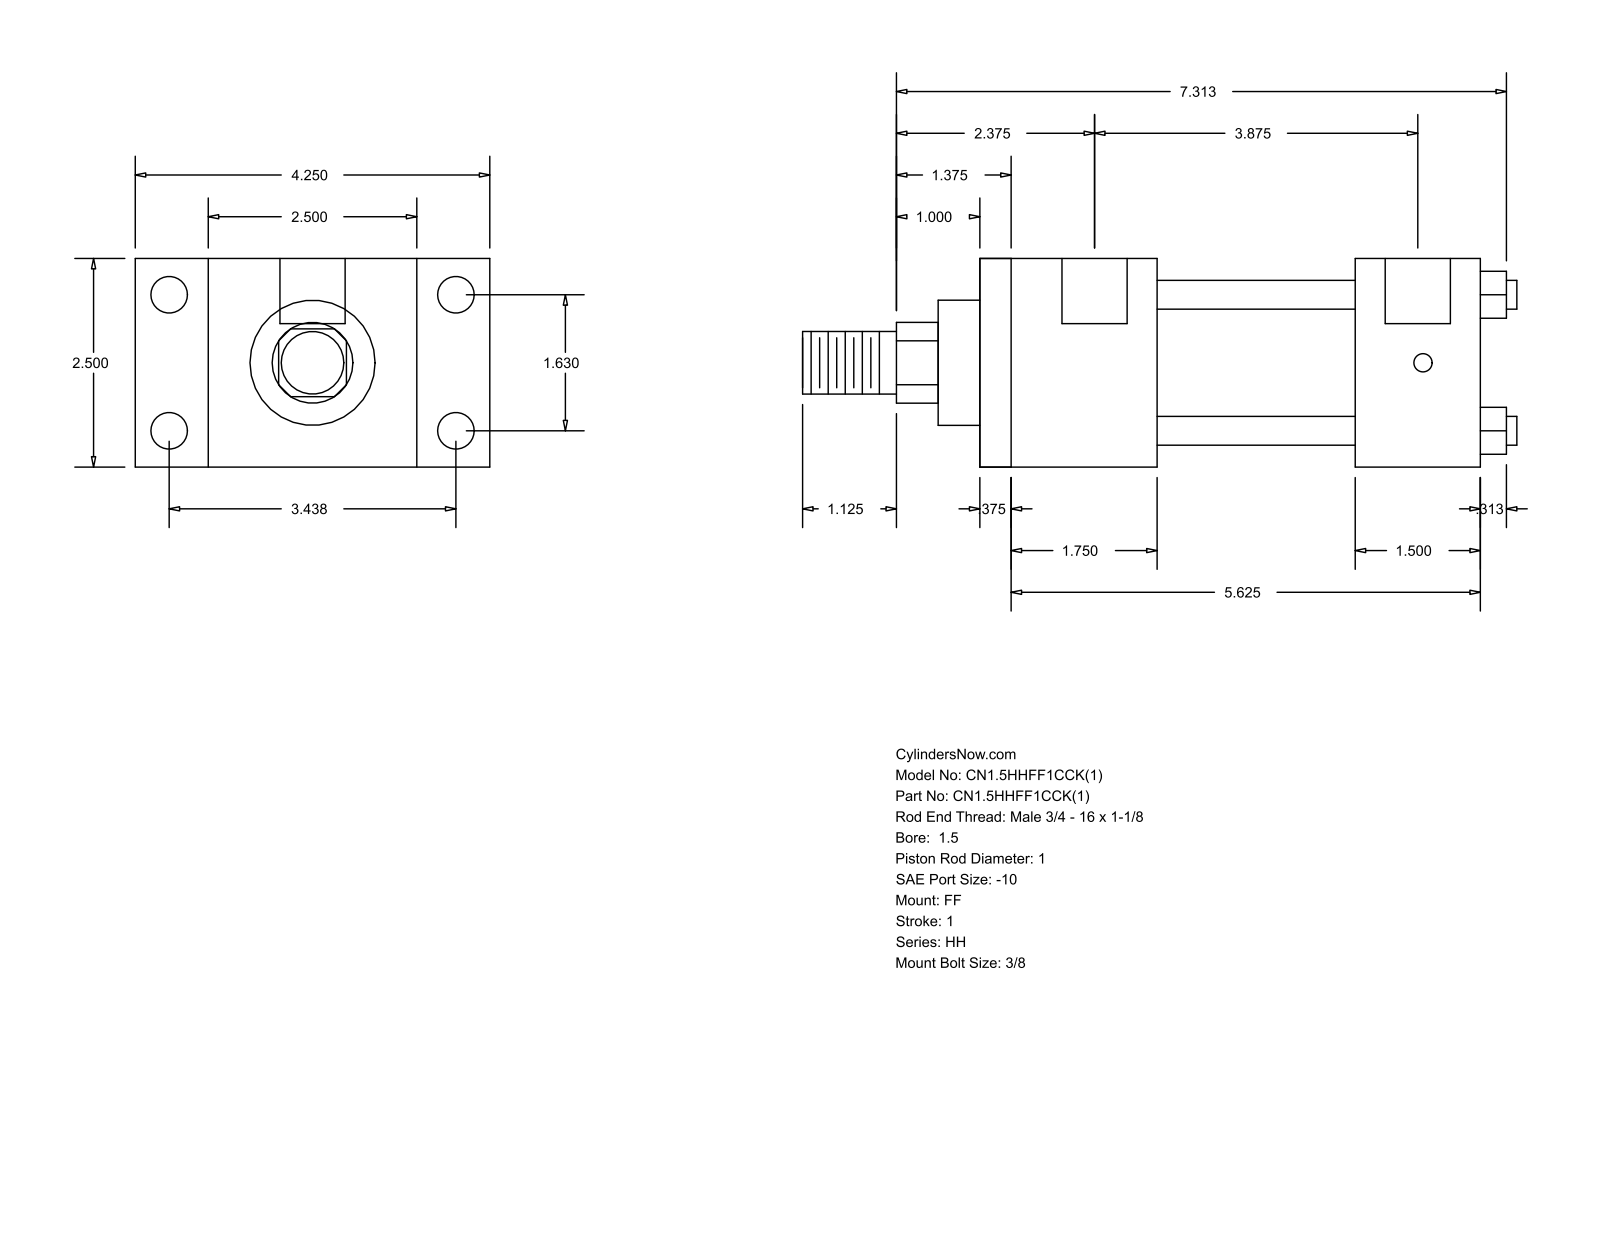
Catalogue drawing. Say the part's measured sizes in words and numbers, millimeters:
The part is named "HH_FF__0150_1". Its 3-D file was written by "GSSL Pune (CONFIG_CONTROL_DESIGN)". It is 0 solids with 92 faces: 64 planar, 28 cylindrical and 0 other. Overall it measures 217.49 by 107.95 by 63.5 millimeters. Round holes: 4 of diameter 5.56, 4 of diameter 11.13, 2 of diameter 19.84. Round bosses or shafts: 4 of diameter 8.76, 1 of diameter 44.45, 1 of diameter 38.1, 1 of diameter 25.4, 1 of diameter 19.05. Partial cylindrical surfaces (rounded edges, fillets, slot ends): 1 of radius 12.29. The main face-to-face distances are 63.5, 152.4, 9.52, 142.88, 38.1, 53.98, 44.46, 98.42, 114.3, 104.78. The hole center spacings are 1.59, 41.4, 87.32, 96.64, 100.01, 101.6, 98.42.
